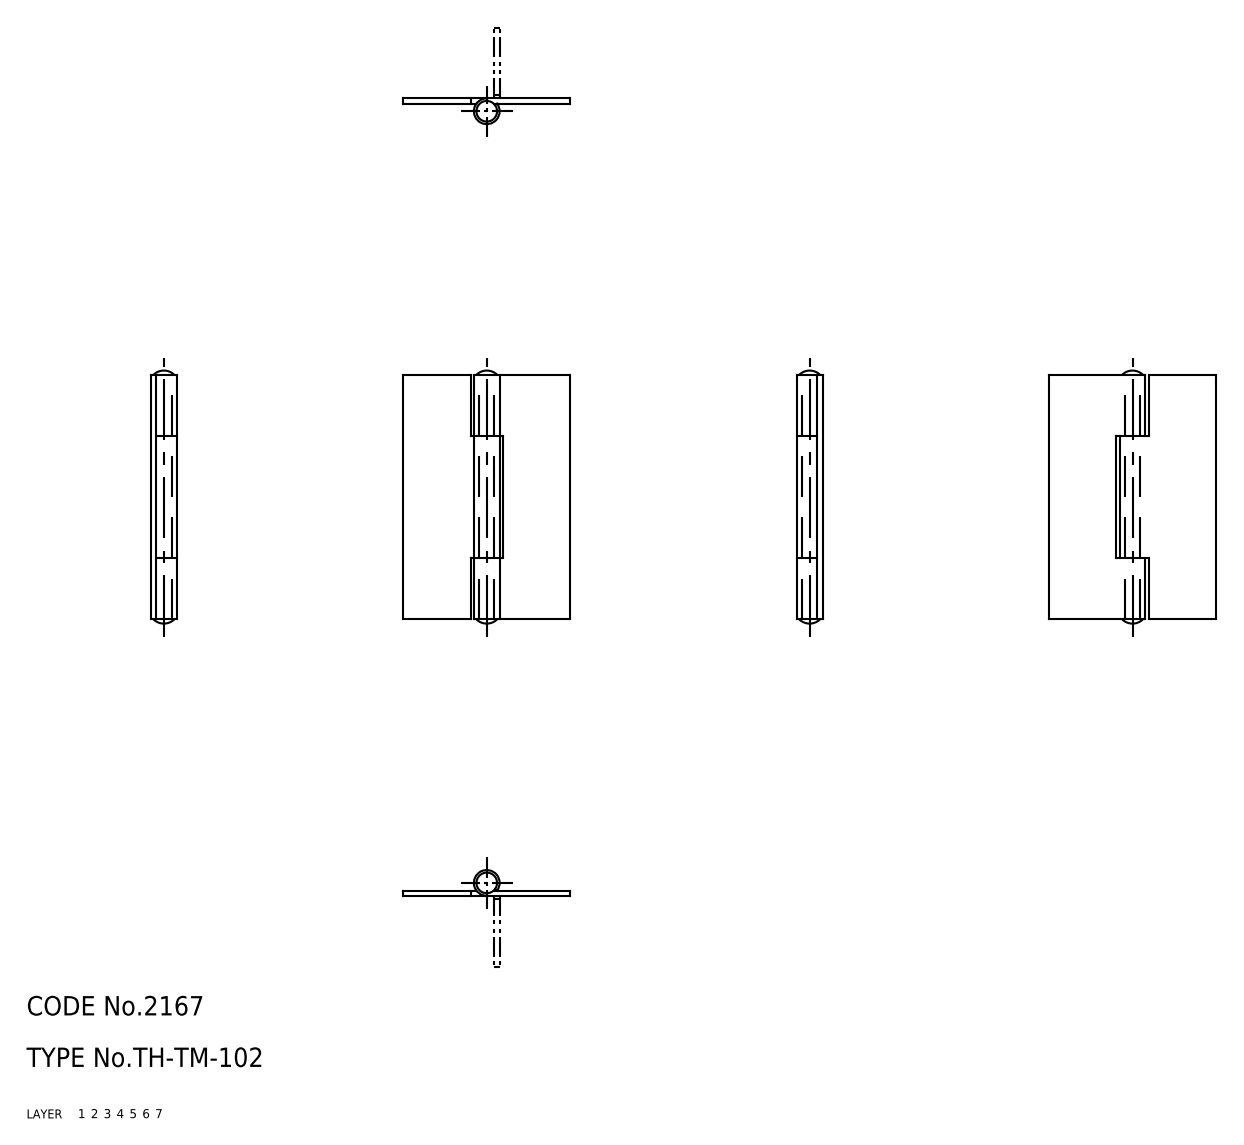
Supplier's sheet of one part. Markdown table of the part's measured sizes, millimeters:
| quantity | value |
| --- | --- |
| part name | 67110372; 67110385; 67110398 |
| STEP written by | CADfix (AUTOMOTIVE_DESIGN) |
| units | millimeters |
| bodies | 3 solids, 32 faces (0 planar, 0 cylindrical, 32 other) |
| overall size | 39.3 × 26 × 4 |
| volume | 1 151 mm³ |
| surface area | 2 954 mm² |
